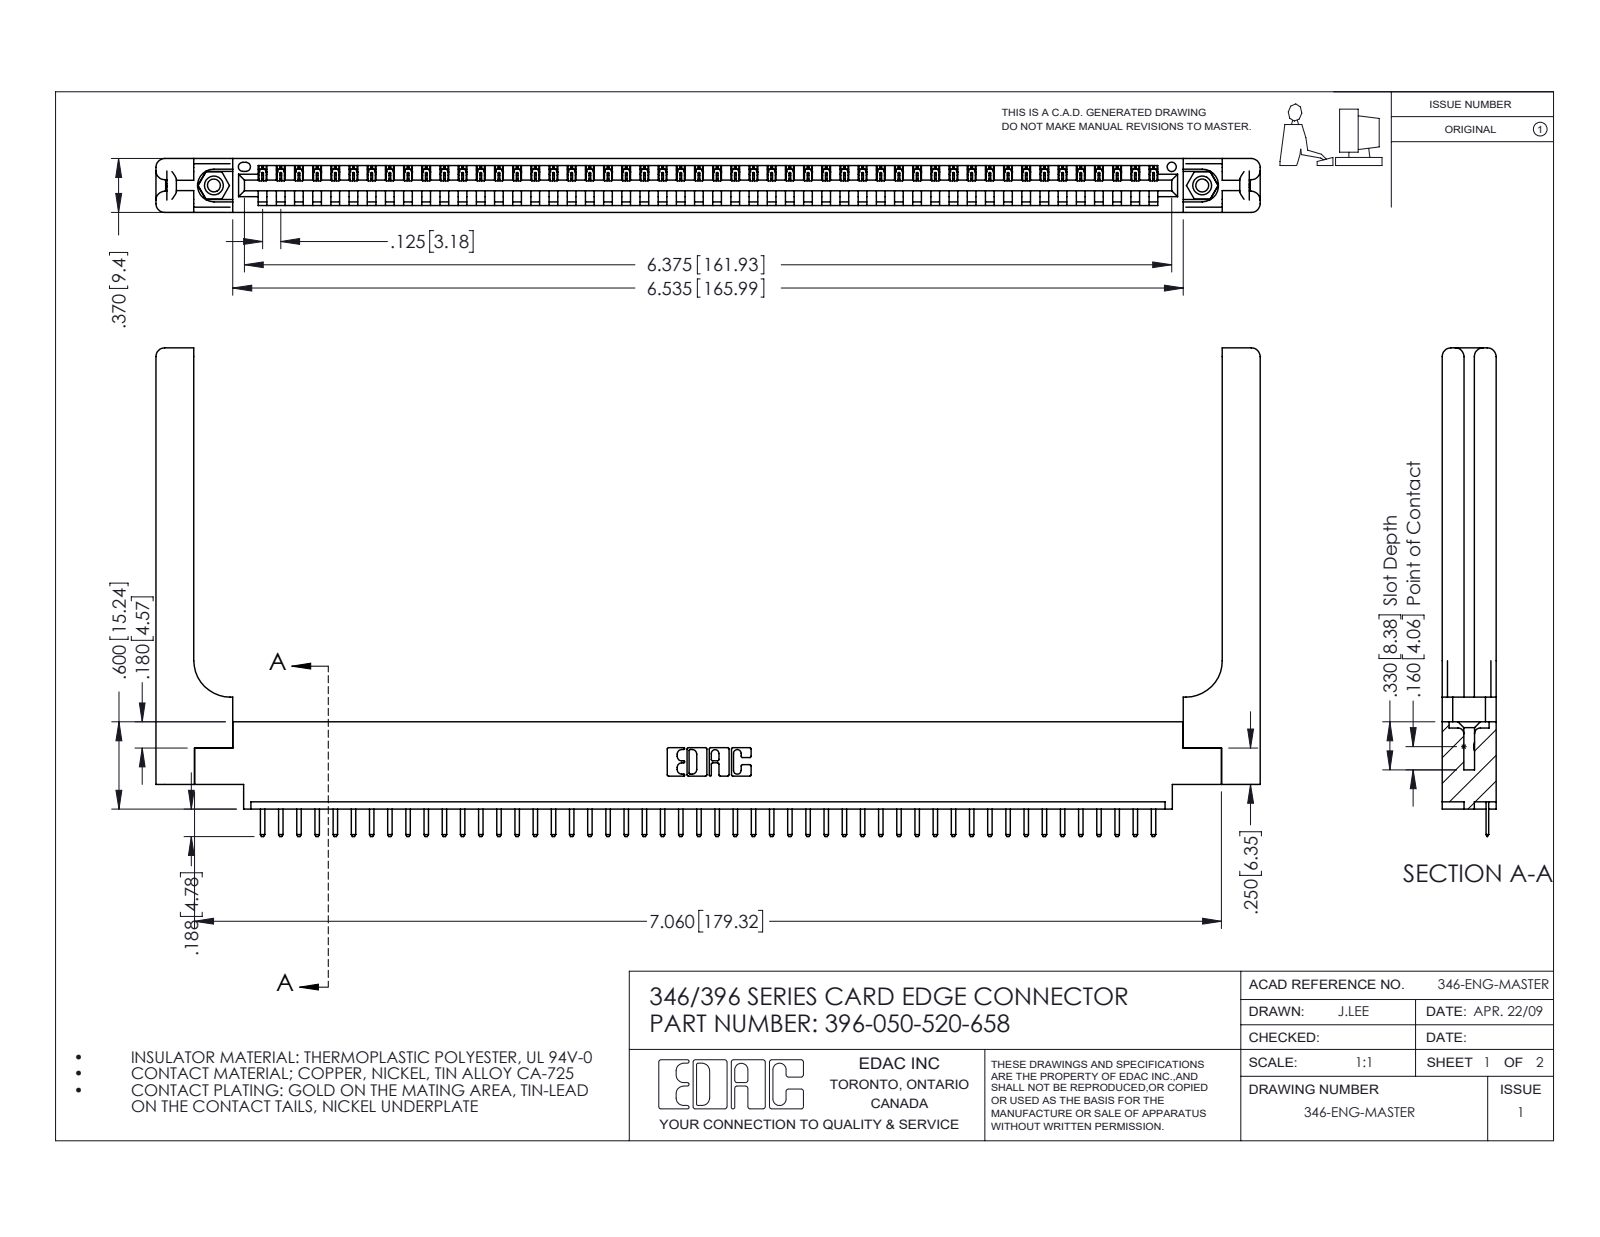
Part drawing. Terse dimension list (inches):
name: 396-050-520-658; 346-220-058_345-220-058; 346 Part_0.170 Offset - 0.156 Dia-TH; 345-250-001_345-250-001-102 (+1 more)
written by: SolidWorks 2016 (CONFIG_CONTROL_DESIGN)
unit: in
bodies: 55 solids, 3482 faces (2328 planar, 1094 cylindrical, 60 other)
size: 7.591 × 3.358 × 0.37
volume: 1.57 in³; area: 42.94 in²
holes: 2× ⌀0.089, 2× ⌀0.125, 2× ⌀0.156, 1× ⌀0.064
bosses: 2× ⌀0.155
rounds: 102× R0.01, 100× R0.006, 22× R0.01, 16× R0.06, 6× R0.007, 6× R0.031, 3× R0.026, 2× R0.03
face distances: 0.37, 0.048, 0.322, 0.072, 0.148, 0.15, 0.25, 0.298, 0.025, 0.222
hole spacings: 0.246, 6.586, 6.795
